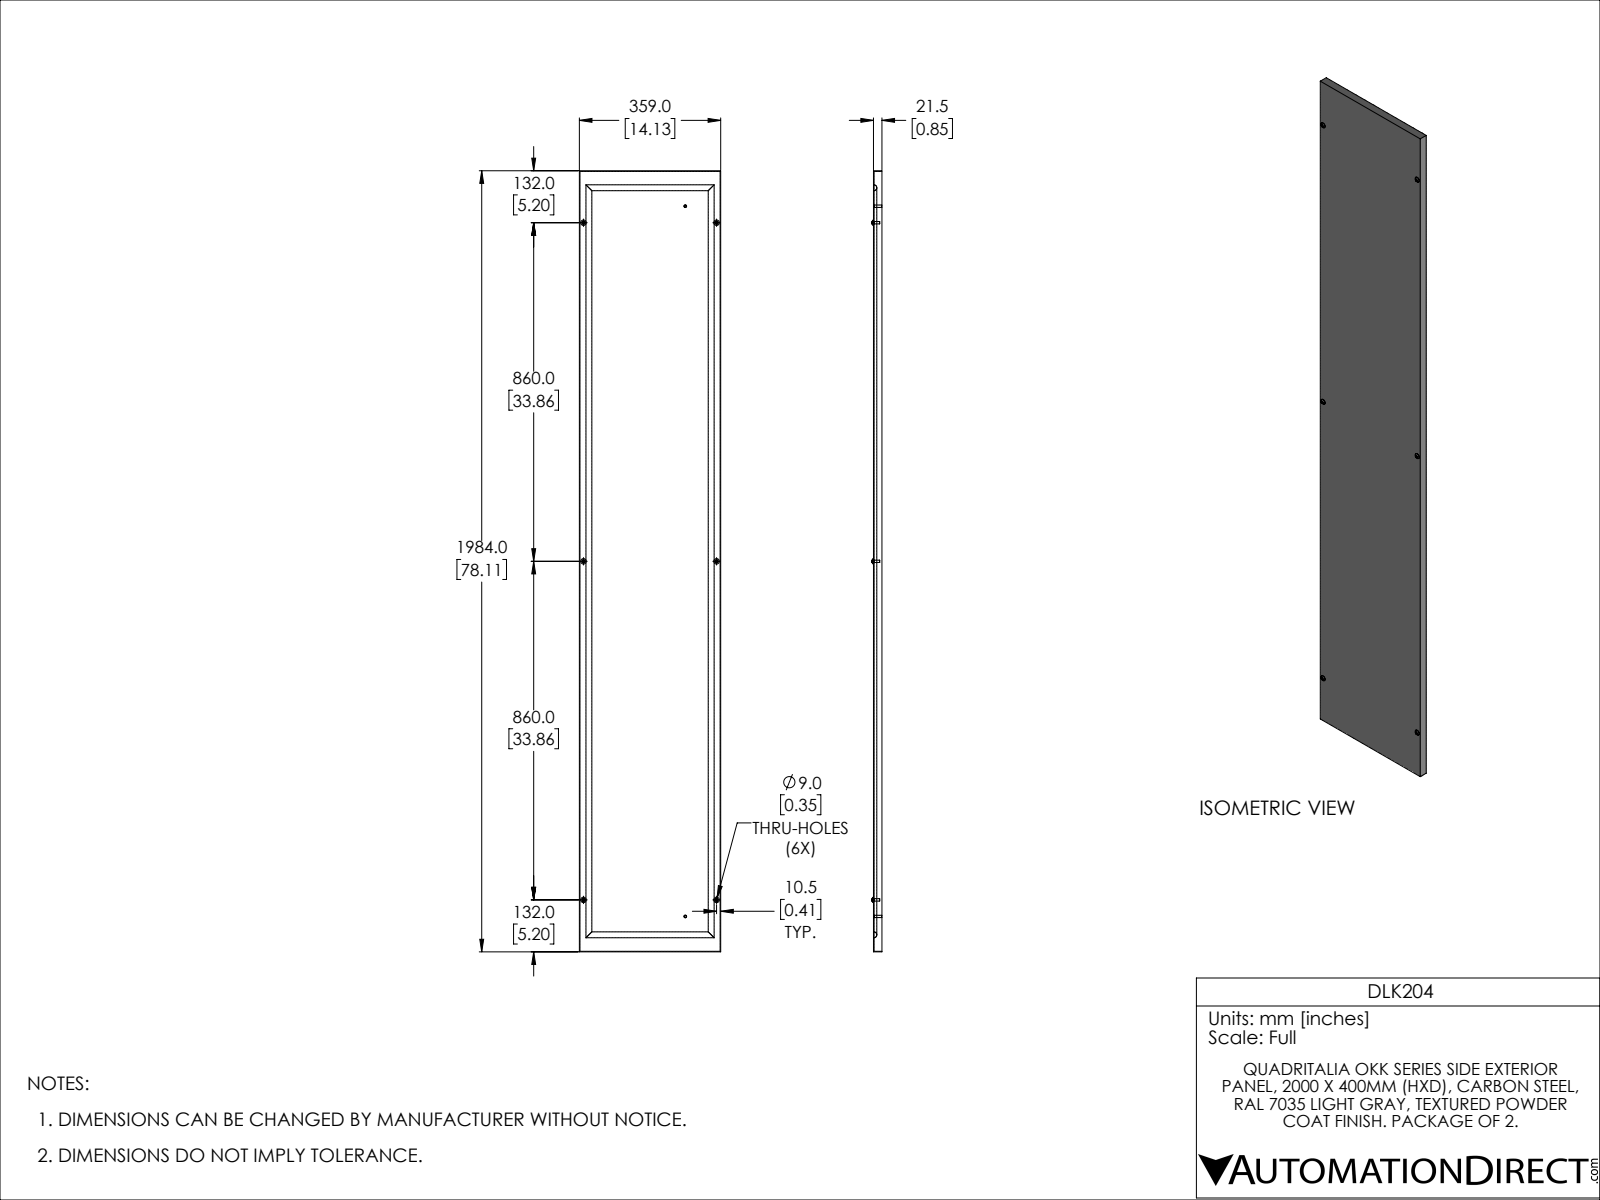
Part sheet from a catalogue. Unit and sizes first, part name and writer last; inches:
Units: inches
Overall size (bounding box): 78.11 × 14.134 × 0.992
Round holes (diameter × count): ⌀0.354 ×6
Round bosses / shafts (diameter × count): ⌀0.236 ×8, ⌀0.551 ×6, ⌀0.276 ×2
Partial cylindrical surfaces — rounded edges, fillets, slot ends (radius × count): R0.02 ×72, R0.296 ×4
Main face-to-face distances: 0.059, 14.075, 14.134, 14.016, 78.051, 78.11, 77.992, 0.846, 0.787, 44.173
Hole centre spacings: 33.858, 36.38, 13.307, 67.717, 69.012
Volume: 95.91 in³ · Surface area: 2 775 in²
Bodies: 13 solids, 243 faces (125 planar, 98 cylindrical, 20 other)
Part name (STEP PRODUCT): DLK204
STEP written by: SolidWorks 2021 (CONFIG_CONTROL_DESIGN)
